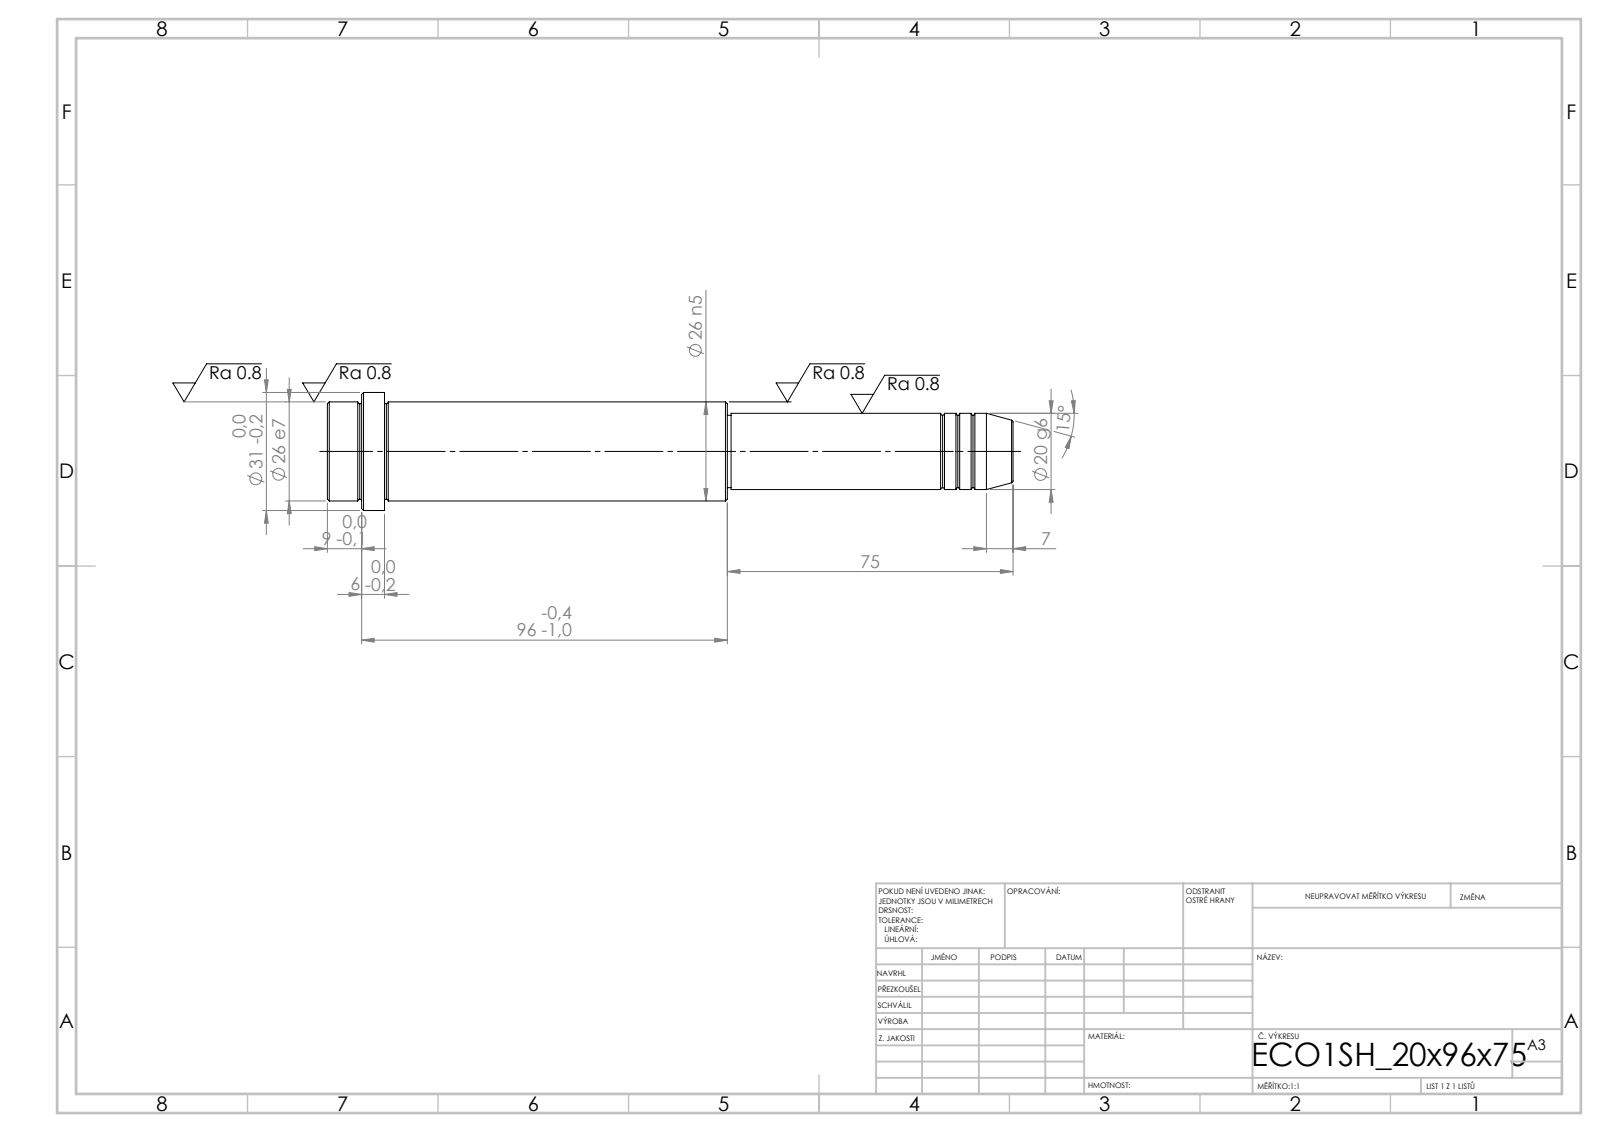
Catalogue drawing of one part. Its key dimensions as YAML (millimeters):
step_written_by: "SolidWorks 2019 (CONFIG_CONTROL_DESIGN)"
units: millimeters
bodies: {solids: 1, faces: 52, planar: 6, cylindrical: 16, other: 30}
overall_size: [180, 31, 31]
volume: 80066
surface_area: 14919
round_bosses_or_shafts:
  - {diameter: 31, count: 1}
  - {diameter: 26, count: 1}
  - {diameter: 20, count: 1}
  - {diameter: 19, count: 1}
face_to_face_distances: [15, 90, 105, 75, 165, 180, 171, 96, 6, 9]
